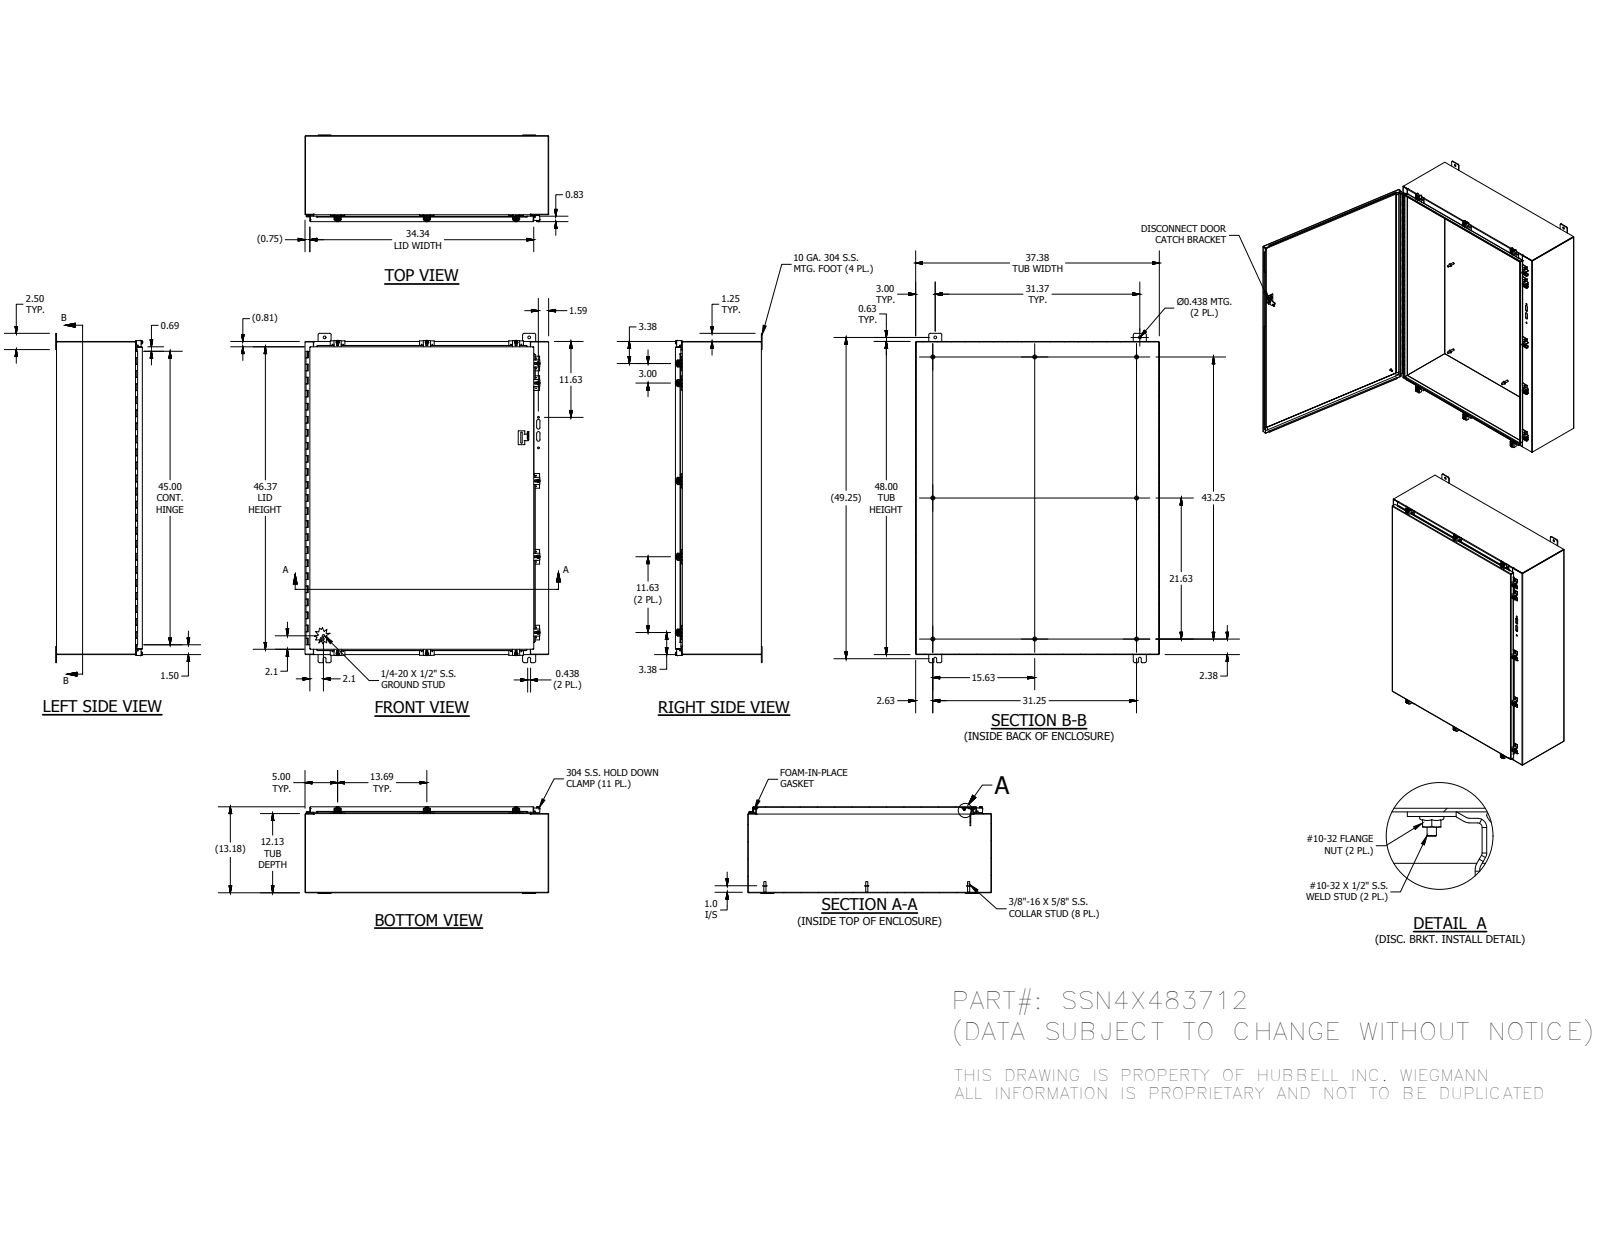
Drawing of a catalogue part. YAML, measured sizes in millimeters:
part_name: "SSN4X483712BLR; 38859; 34871; H6050558T (+8 more)"
step_written_by: "Autodesk Inventor 2016 (AUTOMOTIVE_DESIGN)"
units: millimeters
bodies: {solids: 70, faces: 2438, planar: 1262, cylindrical: 688, other: 488}
overall_size: [1282.7, 949.33, 337.85]
volume: 7940000
surface_area: 8195000
round_holes:
  - {diameter: 2.79, count: 22}
  - {diameter: 5.36, count: 11}
  - {diameter: 7.16, count: 11}
  - {diameter: 11.13, count: 4}
  - {diameter: 3.96, count: 2}
  - {diameter: 7.14, count: 2}
  - {diameter: 3.17, count: 1}
round_bosses_or_shafts:
  - {diameter: 15.88, count: 19}
  - {diameter: 6.35, count: 13}
  - {diameter: 13.21, count: 11}
  - {diameter: 8.89, count: 11}
  - {diameter: 5.04, count: 11}
  - {diameter: 0.76, count: 10}
  - {diameter: 8.38, count: 8}
  - {diameter: 8.56, count: 3}
partial_cylinders:
  - {radius: 0.76, count: 89}
  - {radius: 6.35, count: 39}
  - {radius: 3.17, count: 27}
  - {radius: 0.79, count: 25}
  - {radius: 3.62, count: 22}
  - {radius: 2.67, count: 21}
  - {radius: 1.59, count: 17}
  - {radius: 1.35, count: 16}
face_to_face_distances: [1.88, 332.79, 330.91, 334.67, 1217.32, 1.87, 945.57, 947.44, 947.45, 949.32]
hole_center_spacings: [1204.5, 22.26, 347.66, 368.39, 1245.49, 1247.93, 1259.38, 327.13]
